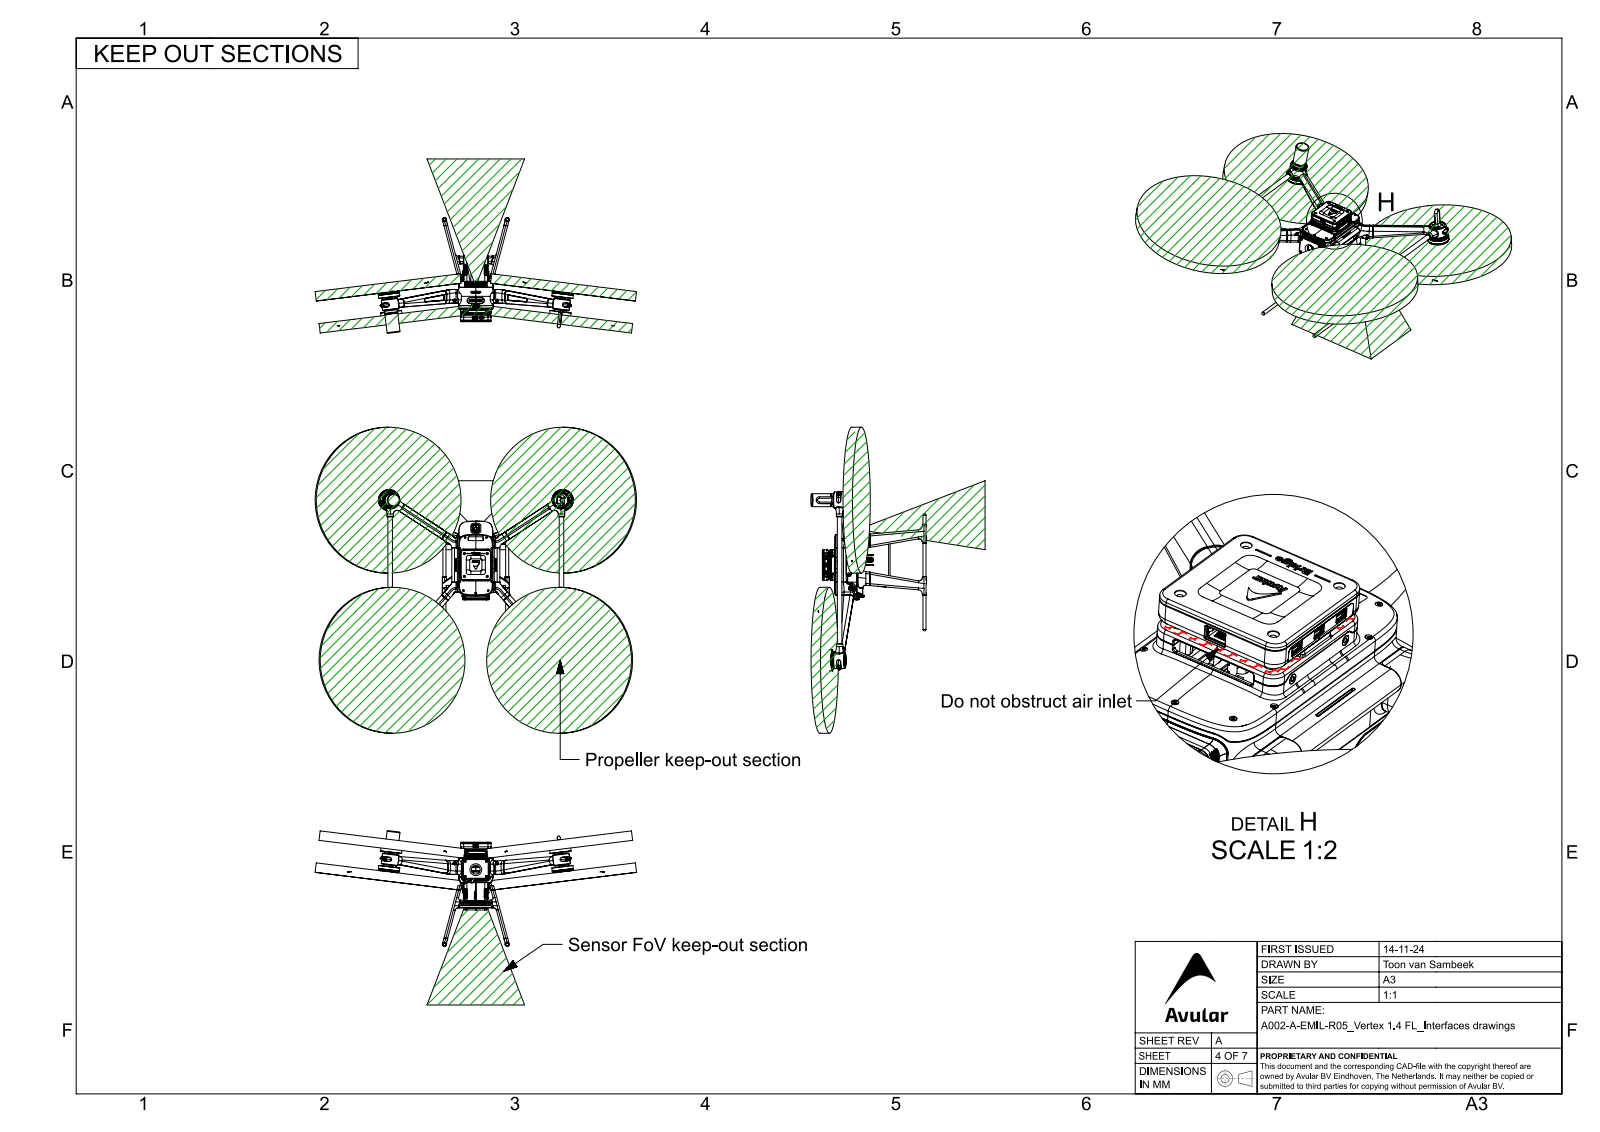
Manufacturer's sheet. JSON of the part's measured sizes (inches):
{"part_name": "KEEP OUT SECTIONS-A002-A-EMIL-R05_Vertex 1.4 FL_objects", "step_written_by": "SIEMENS PLM Software NX2206.1700 (AUTOMOTIVE_DESIGN)", "units": "inches", "bodies": {"solids": 141, "faces": 24123, "planar": 13836, "cylindrical": 5885, "other": 4402}, "overall_size": [33.222, 31.614, 18.014], "volume_in3": 1022, "surface_area_in2": 2917, "round_holes": [[0.098, 30], [0.024, 24], [0.014, 14], [0.256, 12], [0.157, 11], [0.035, 10], [0.014, 8], [0.134, 8], [2.071, 8], [0.217, 4], [0.244, 4], [0.26, 4]], "round_bosses_or_shafts": [[0.036, 24], [0.018, 24], [0.016, 12], [2.189, 8], [0.118, 6], [0.028, 6], [0.022, 6], [0.236, 5]], "partial_cylinders_radius": [[0.059, 487], [0.008, 446], [0.006, 335], [0.039, 293], [0.02, 276], [0.079, 203], [0.01, 185], [0.012, 150]], "face_to_face_distances": [0.985, 0.985, 2.343, 3.328, 3.328, 4.313, 1.24, 1.236, 0.071, 0.38], "hole_center_spacings": [0.236, 0.354, 0.05, 3.492, 0.501, 0.1, 3.493, 0.2]}
